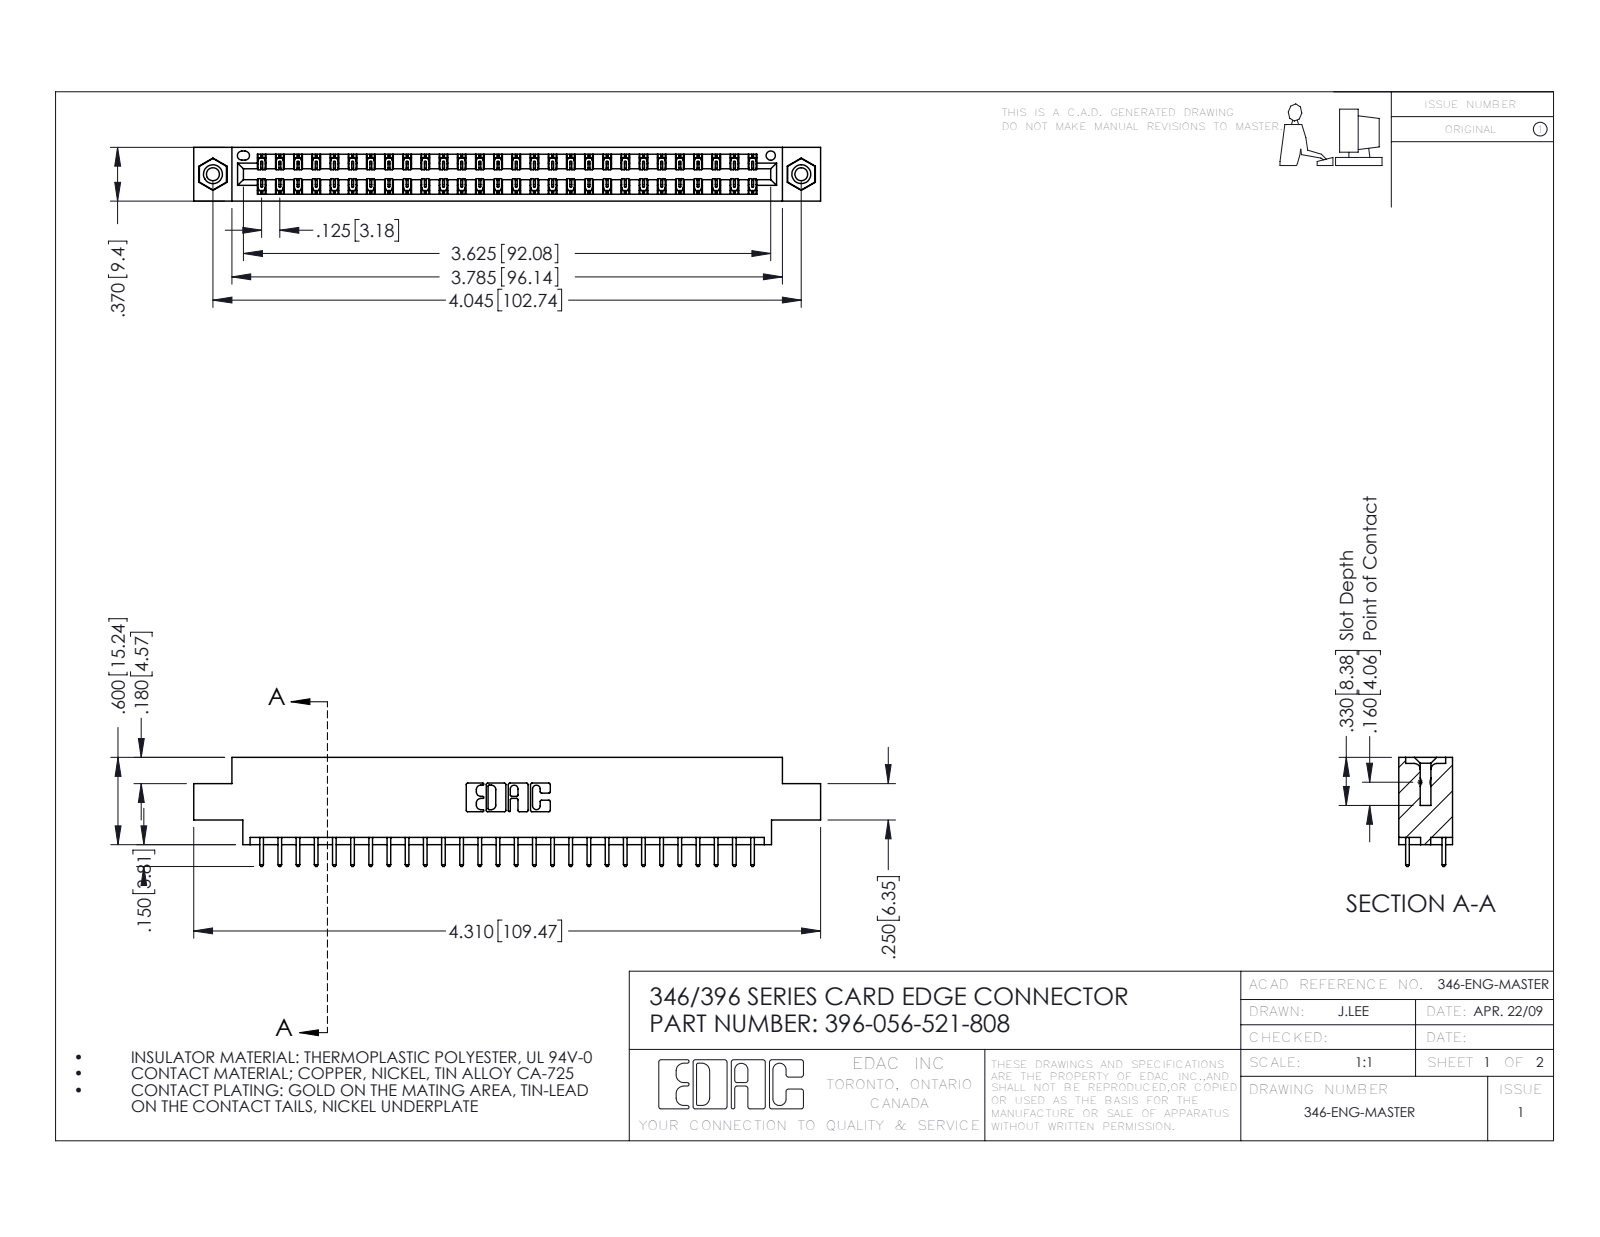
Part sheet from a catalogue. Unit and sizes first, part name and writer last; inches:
Units: inches
Overall size (bounding box): 4.31 × 0.75 × 0.37
Round holes (diameter × count): ⌀0.089 ×2, ⌀0.125 ×2, ⌀0.156 ×2, ⌀0.064 ×1
Round bosses / shafts (diameter × count): ⌀0.155 ×2
Partial cylindrical surfaces — rounded edges, fillets, slot ends (radius × count): R0.006 ×84, R0.01 ×56, R0.01 ×22, R0.007 ×6, R0.031 ×6, R0.026 ×3, R0.014 ×2, R0.022 ×2
Main face-to-face distances: 0.048, 0.322, 0.37, 0.25, 0.072, 0.298, 0.025, 0.275, 0.222, 0.148
Hole centre spacings: 0.246, 3.837, 4.045
Volume: 0.634 in³ · Surface area: 21.85 in²
Bodies: 59 solids, 3098 faces (2072 planar, 1010 cylindrical, 16 other)
Part name (STEP PRODUCT): 345-292-001_345-293-121; 345-250-001_345-250-003-102; 346 Part_0.170 Offset - 0.156 Dia-TI; 396-056-521-808
STEP written by: SolidWorks 2016 (CONFIG_CONTROL_DESIGN)
